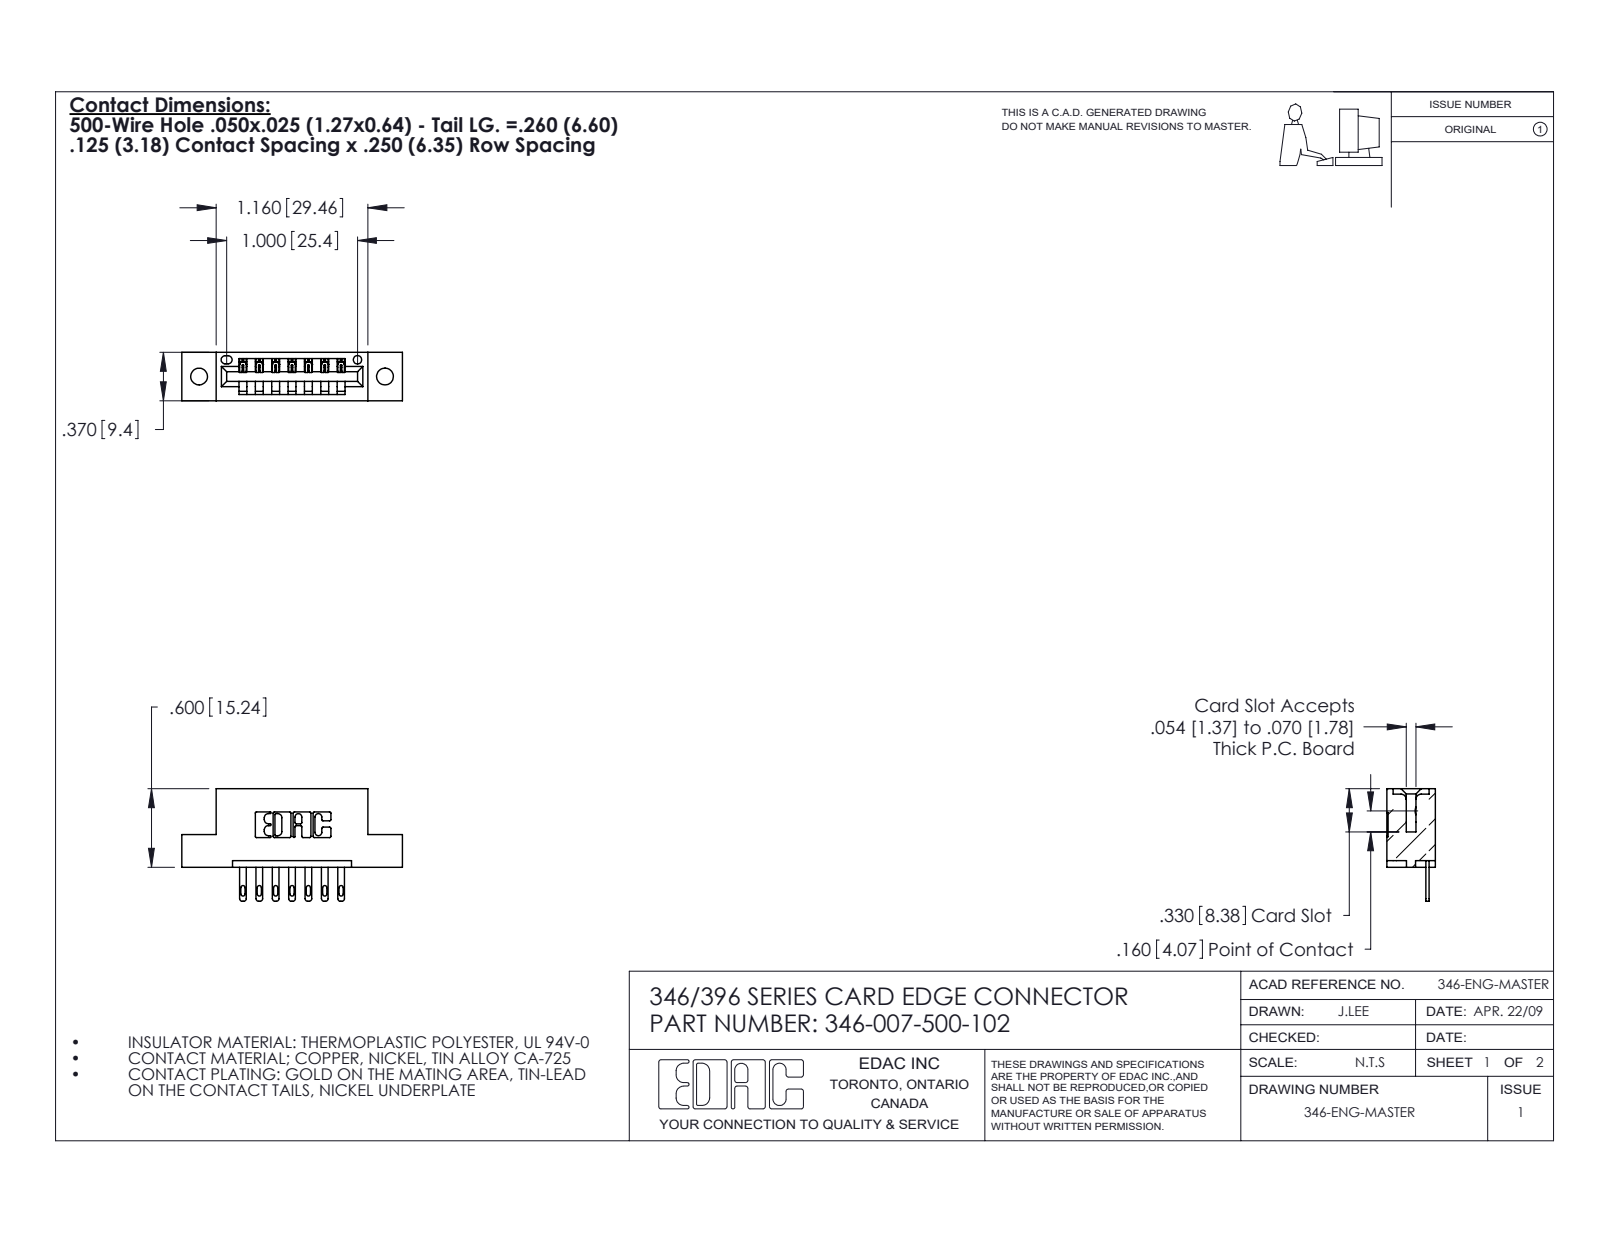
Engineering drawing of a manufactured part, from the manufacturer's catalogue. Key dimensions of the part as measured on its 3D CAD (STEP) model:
Part name (STEP PRODUCT): 345-292-001_345-293-100; 346-007-500-102; 346 Part_Flush Mounting Lugs - 0.128 Dia
STEP written by: SolidWorks 2020 (CONFIG_CONTROL_DESIGN)
Units: inches
Bodies: 8 solids, 500 faces (314 planar, 186 cylindrical, 0 other)
Overall size (bounding box): 1.685 × 0.86 × 0.37
Volume: 0.233 in³ · Surface area: 6.426 in²
Round holes (diameter × count): ⌀0.128 ×2, ⌀0.064 ×1
Partial cylindrical surfaces — rounded edges, fillets, slot ends (radius × count): R0.01 ×22, R0.006 ×14, R0.016 ×14, R0.02 ×14, R0.007 ×6, R0.031 ×6, R0.026 ×3, R0.031 ×2
Main face-to-face distances: 0.25, 0.37, 0.048, 0.322, 0.072, 0.298, 0.025, 0.148, 0.222, 0.1
Hole centre spacings: 0.246, 1.217, 1.42
